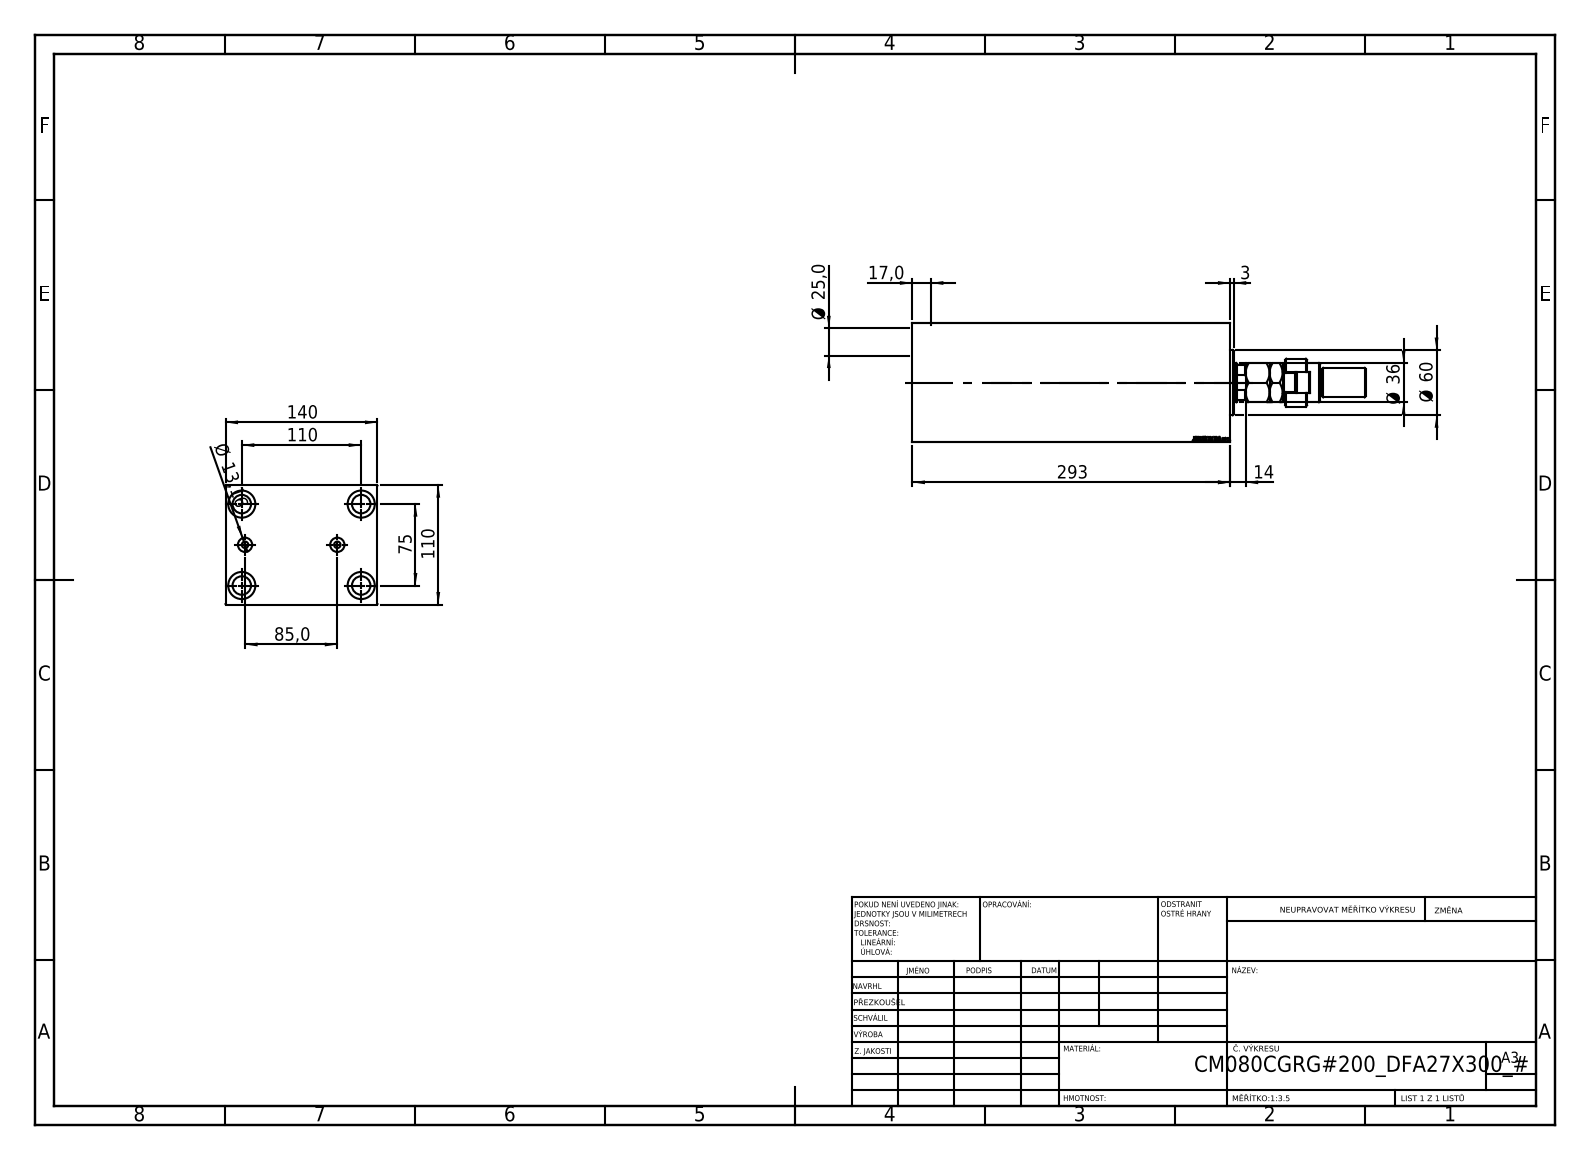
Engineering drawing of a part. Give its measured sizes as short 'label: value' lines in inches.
name: V450CM_VC_B; FEMALE_PART_FOR_DFA; V450CM_C_Body; MFA (+1 more)
written by: SolidWorks 2019 (CONFIG_CONTROL_DESIGN)
unit: in
bodies: 5 solids, 945 faces (436 planar, 71 cylindrical, 438 other)
size: 16.437 × 5.512 × 4.331
volume: 213.4 in³; area: 629.2 in²
holes: 4× ⌀0.669, 4× ⌀0.984, 2× ⌀0.236, 2× ⌀0.518, 1× ⌀1.004, 1× ⌀1.555, 1× ⌀3.15, 1× ⌀3.228, 1× ⌀3.425
bosses: 1× ⌀2.362, 1× ⌀1.732, 1× ⌀1.417, 1× ⌀1.102, 1× ⌀1.063, 1× ⌀0.984, 1× ⌀0.709
rounds: 1× R0.374, 1× R0.591, 1× R0.689
face distances: 4.331, 5.512, 11.535, 10.709, 0.827, 0.551, 10.984, 10.157, 8.425, 7.874
hole spacings: 2.621, 1.481, 1.712, 2.953, 3.766, 4.331, 4.464, 5.242
